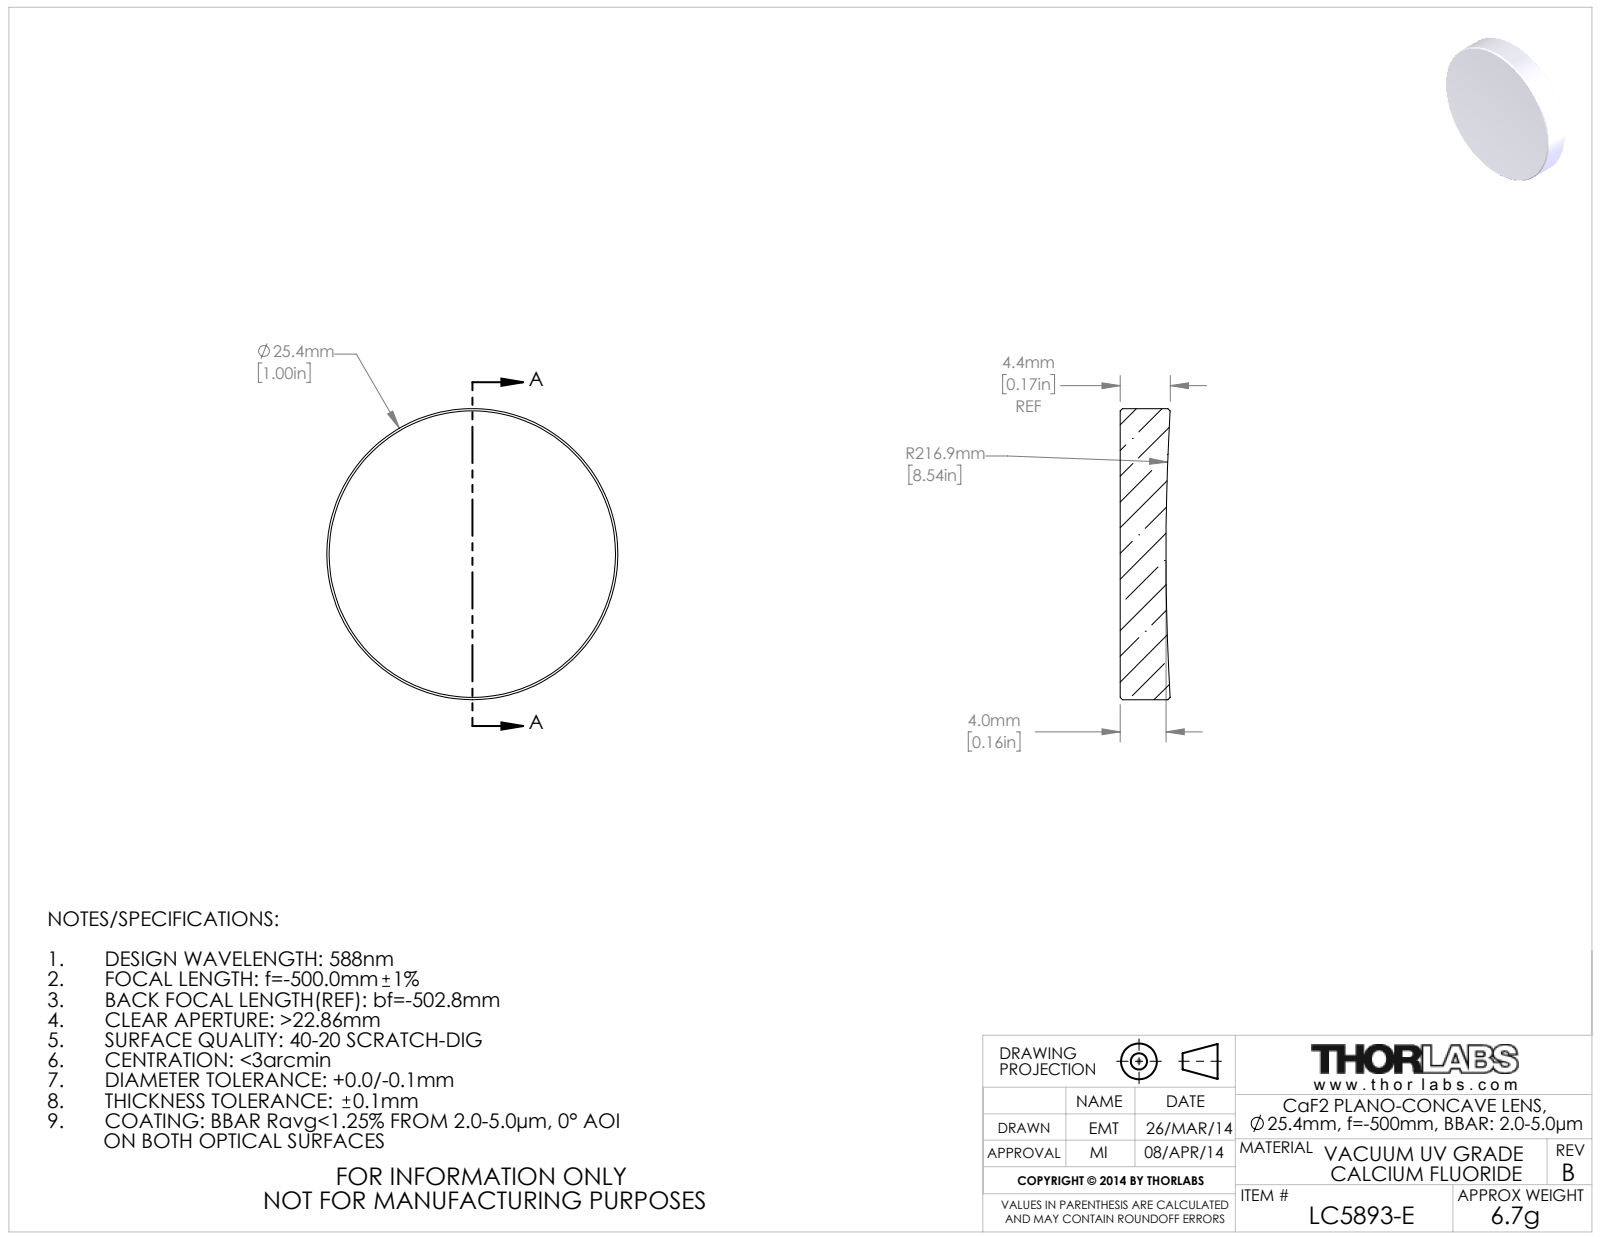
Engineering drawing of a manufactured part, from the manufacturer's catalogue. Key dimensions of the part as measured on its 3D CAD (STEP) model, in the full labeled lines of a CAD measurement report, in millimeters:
Part name (STEP PRODUCT): 20147-E0W
STEP written by: SolidWorks 2016 (CONFIG_CONTROL_DESIGN)
Units: millimetres
Bodies: 1 solid, 9 faces (1 planar, 2 cylindrical, 6 other)
Overall size (bounding box): 25.4 × 25.4 × 4.4
Volume: 2 110 mm³ · Surface area: 1 343 mm²
Round bosses / shafts (diameter × count): ⌀25.4 ×1
